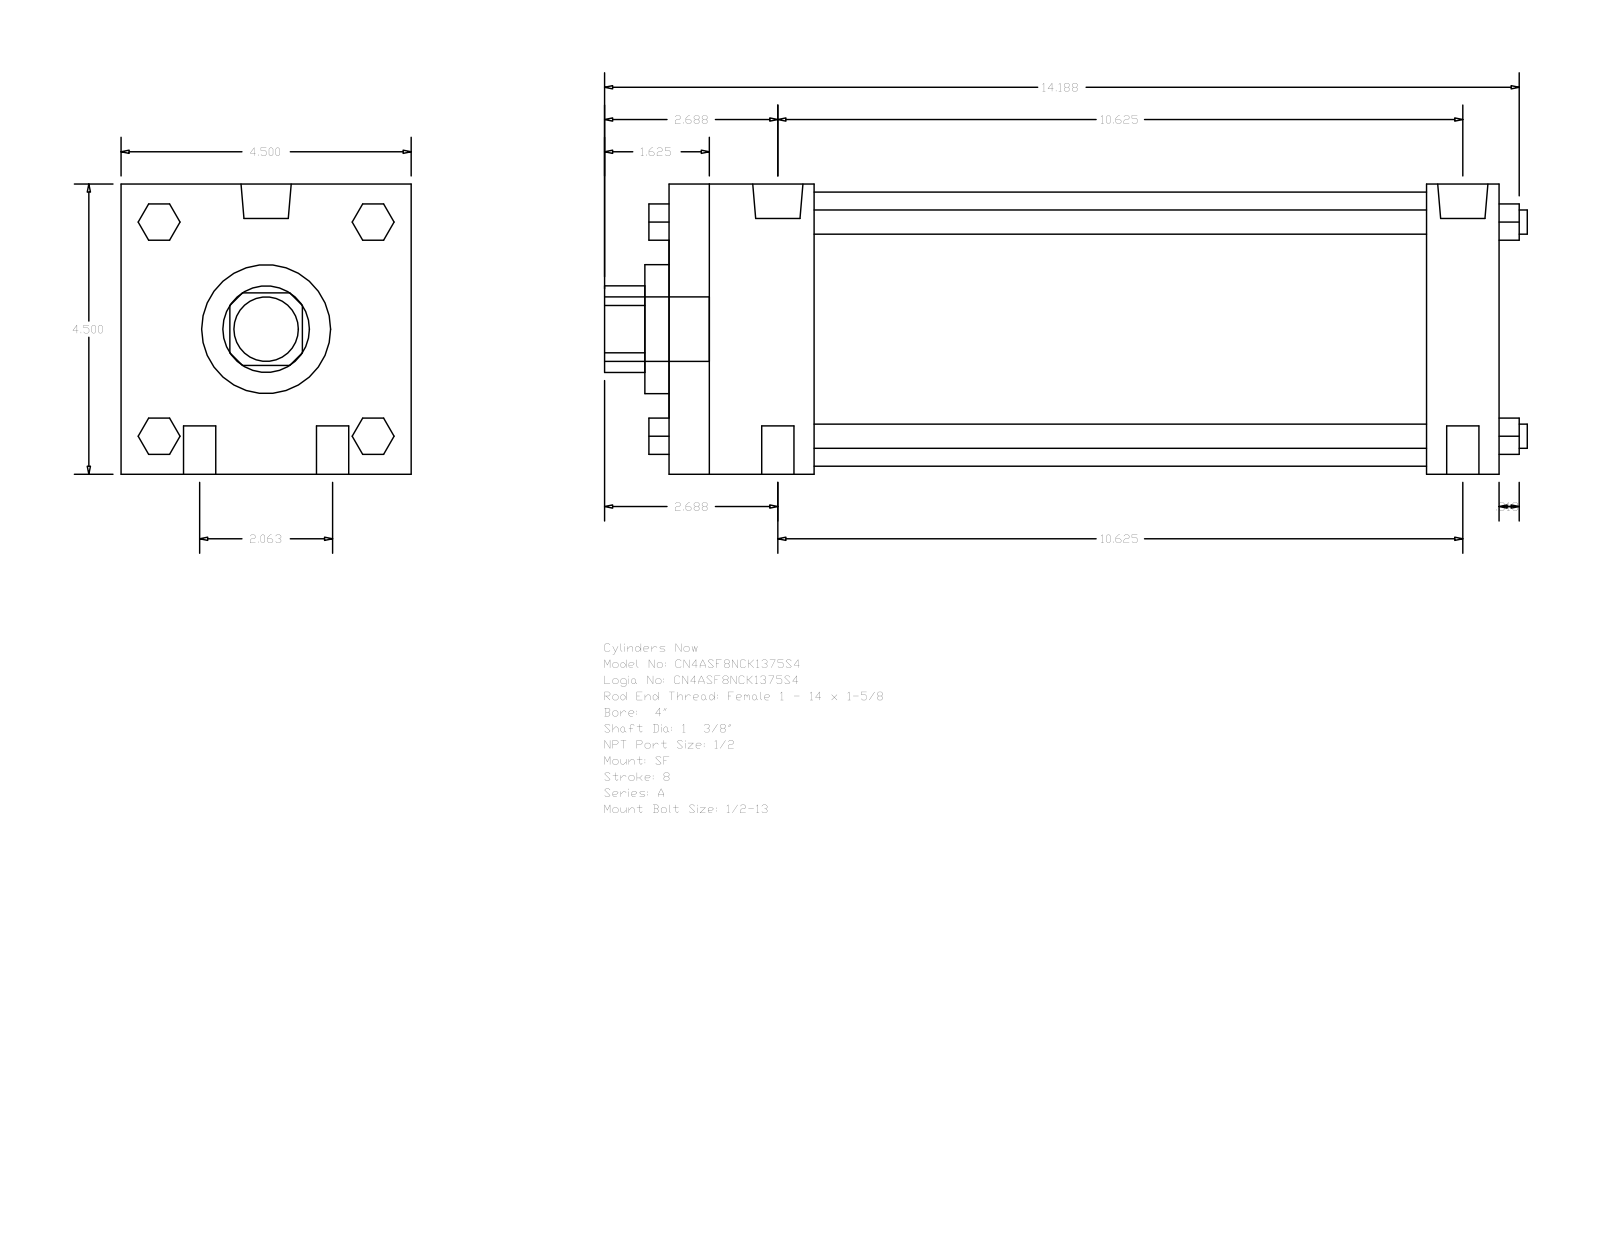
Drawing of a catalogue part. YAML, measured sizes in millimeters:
part_name: "A_SF__0400_1.375"
step_written_by: "GSSL Pune (CONFIG_CONTROL_DESIGN)"
units: millimeters
bodies: {solids: 0, faces: 124, planar: 94, cylindrical: 30, other: 0}
overall_size: [363.54, 114.3, 114.3]
round_holes:
  - {diameter: 34.92, count: 1}
  - {diameter: 50.8, count: 1}
  - {diameter: 107.95, count: 1}
round_bosses_or_shafts:
  - {diameter: 12.7, count: 4}
  - {diameter: 9.53, count: 4}
  - {diameter: 19.77, count: 2}
  - {diameter: 8.73, count: 2}
  - {diameter: 25.4, count: 1}
partial_cylinders:
  - {radius: 17.06, count: 1}
face_to_face_distances: [114.3, 327.03, 28.58, 298.45, 57.15, 241.3, 269.88, 14.29, 9.52, 66.67]
